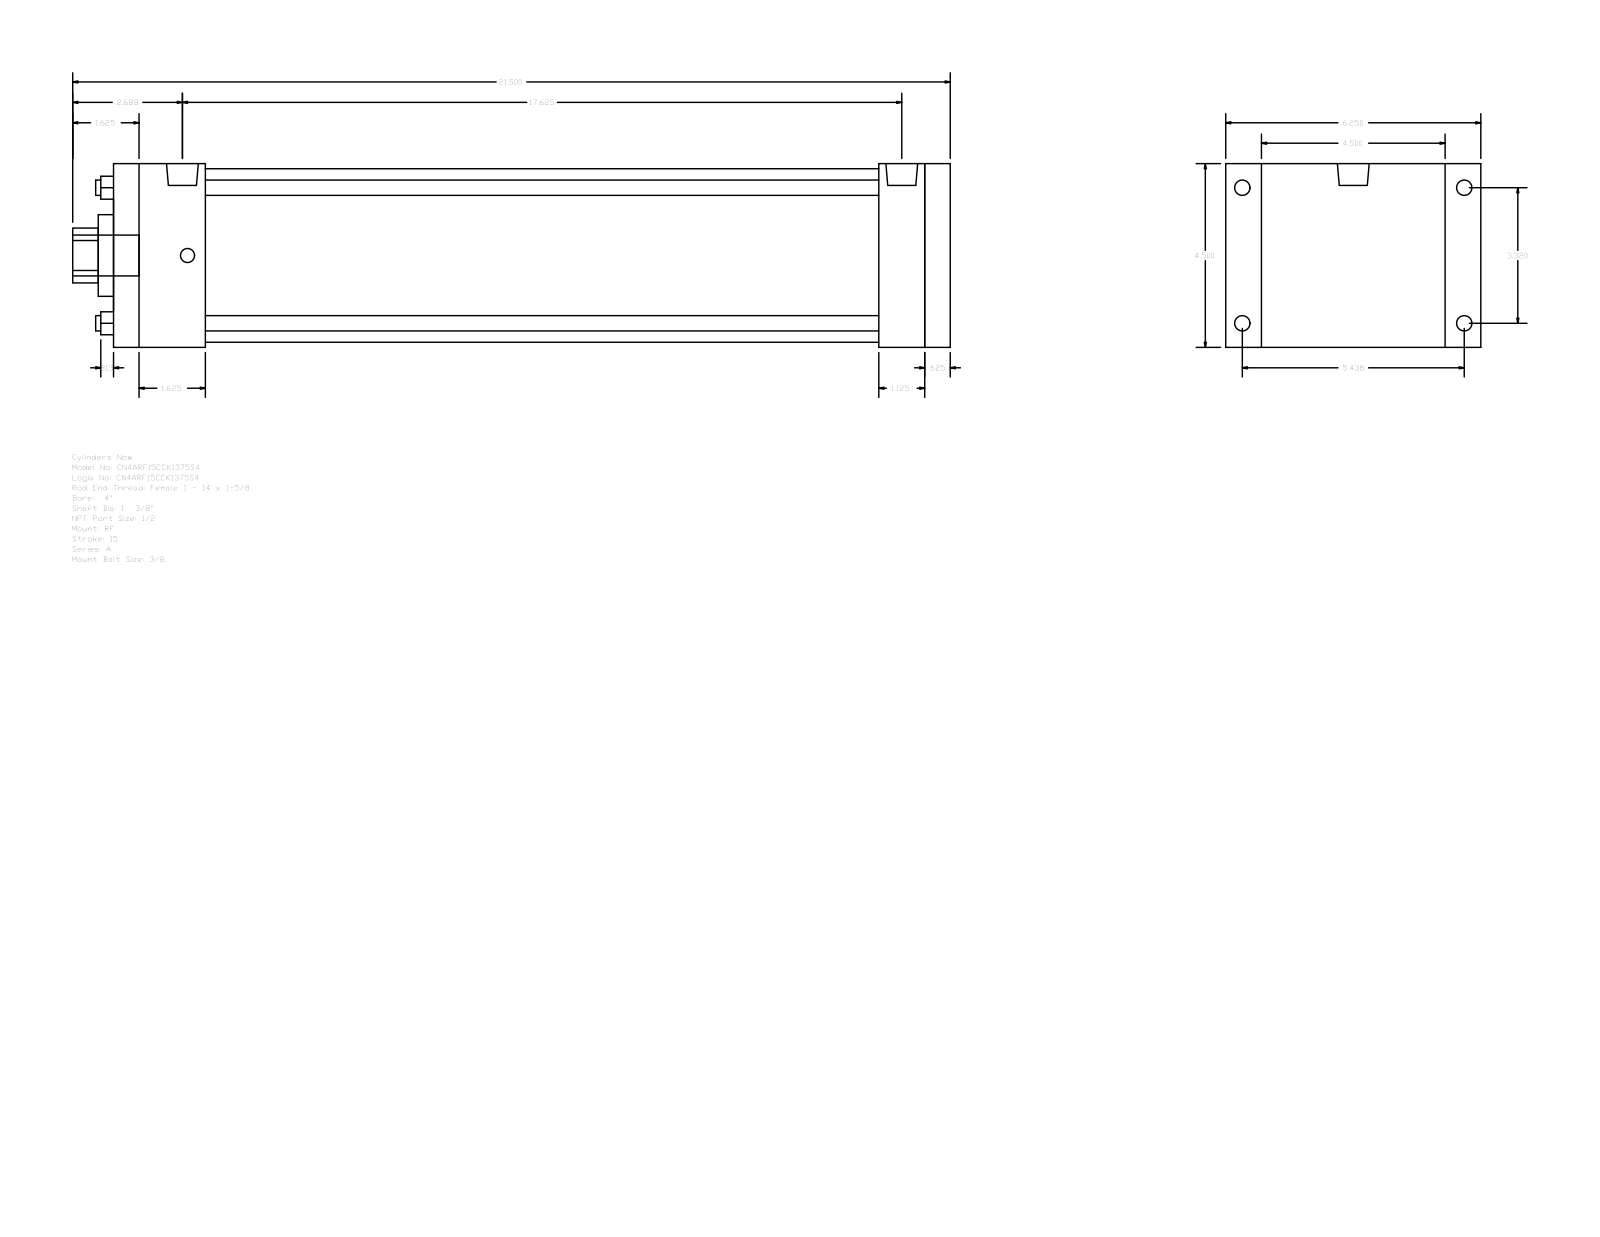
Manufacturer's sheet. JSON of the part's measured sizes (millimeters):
{"part_name": "A_RF__0400_1.375", "step_written_by": "GSSL Pune (CONFIG_CONTROL_DESIGN)", "units": "millimeters", "bodies": {"solids": 0, "faces": 92, "planar": 64, "cylindrical": 28, "other": 0}, "overall_size": [546.1, 158.75, 114.3], "round_holes": [[9.53, 4], [34.92, 1], [50.8, 1], [107.95, 1]], "round_bosses_or_shafts": [[9.53, 4], [8.73, 4], [19.77, 2], [25.4, 1]], "partial_cylinders_radius": [[17.06, 1]], "face_to_face_distances": [114.3, 520.7, 15.87, 504.83, 28.58, 22.23, 136.53, 476.25, 44.45, 57.15], "hole_center_spacings": [59.62, 84.32, 119.25]}
